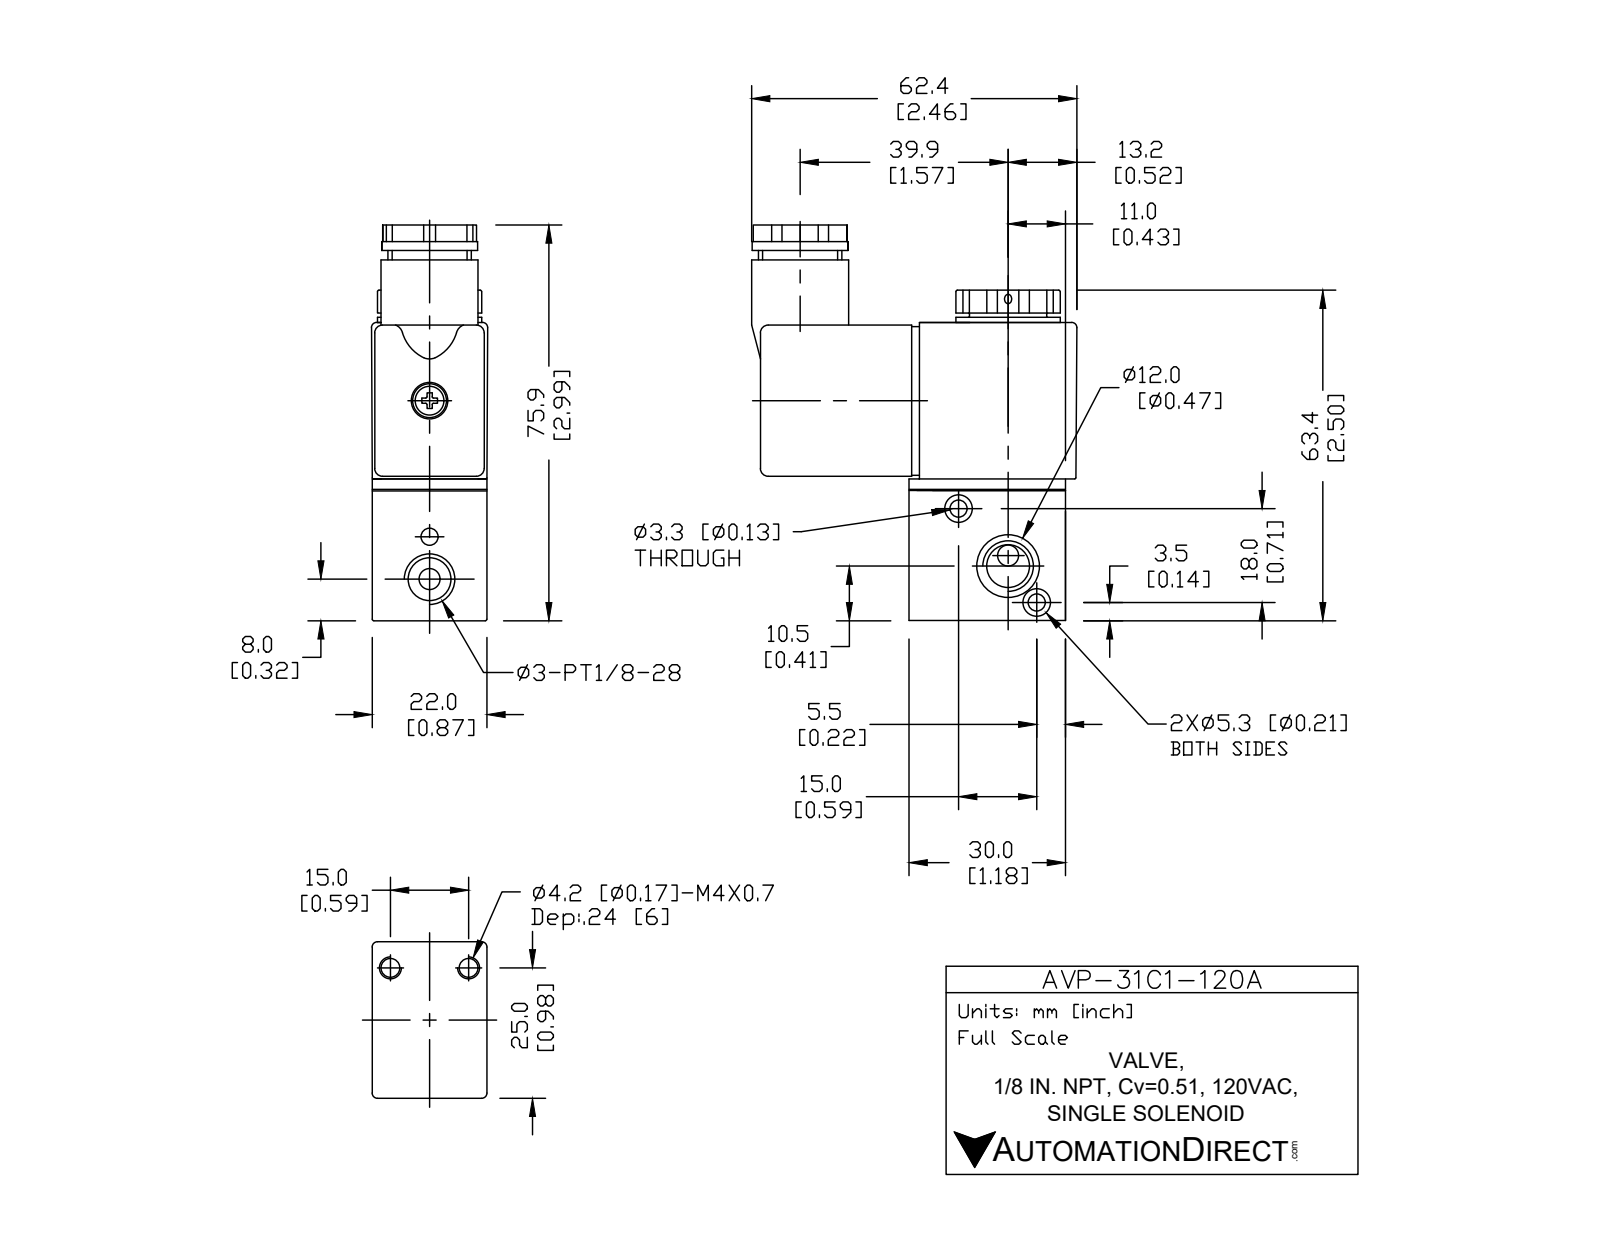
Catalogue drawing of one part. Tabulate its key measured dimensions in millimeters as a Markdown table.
| quantity | value |
| --- | --- |
| part name | AVP-31C1-120A |
| STEP written by | SolidWorks 2017 (AUTOMOTIVE_DESIGN) |
| units | millimeters |
| bodies | 3 solids, 226 faces (102 planar, 103 cylindrical, 21 other) |
| overall size | 75.9 × 62.4 × 22 |
| volume | 59 522 mm³ |
| surface area | 15 836 mm² |
| round holes (diameter × count) | 3.24 × 2, 3.3 × 2, 5.3 × 2, 8.43 × 2, 4 × 1, 7 × 1, 9.3 × 1, 12 × 1 |
| round bosses / shafts (diameter × count) | 20 × 1, 18.6 × 1, 16 × 1, 14 × 1, 6.5 × 1 |
| partial cylindrical surfaces (radius × count) | 0.7 × 36, 1.5 × 17 |
| main face-to-face distances | 22, 0.5, 30, 29.5, 28.5, 58.5, 27.2, 27.7, 60.7, 2.2 |
| hole center spacings | 26.96, 2, 8.9, 10.55, 13.09, 14.53, 15, 23.43 |
